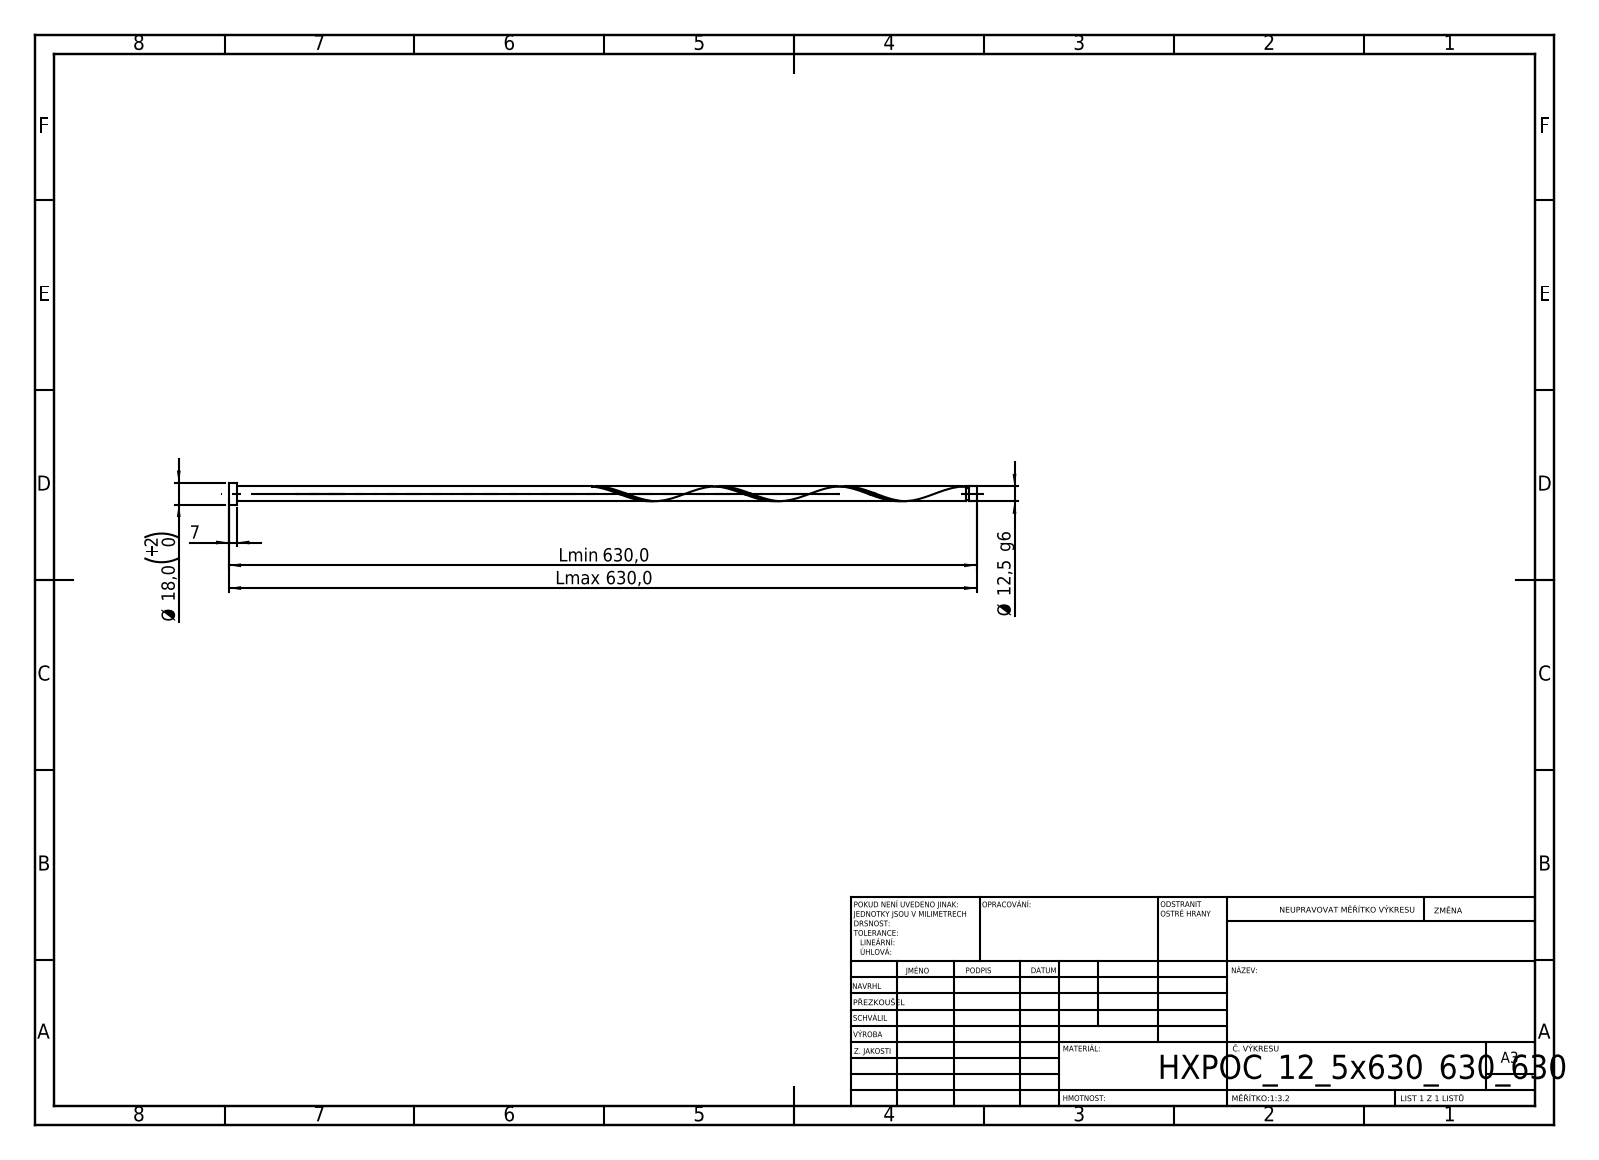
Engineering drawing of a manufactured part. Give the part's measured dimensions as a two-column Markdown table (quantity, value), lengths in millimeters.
| quantity | value |
| --- | --- |
| STEP written by | SolidWorks 2019 (CONFIG_CONTROL_DESIGN) |
| units | millimeters |
| bodies | 1 solid, 21 faces (6 planar, 14 cylindrical, 1 other) |
| overall size | 630 × 18 × 18 |
| volume | 77 384 mm³ |
| surface area | 25 845 mm² |
| round bosses / shafts (diameter × count) | 18 × 1, 12.5 × 1, 10 × 1 |
| main face-to-face distances | 7, 630, 623, 623.26, 616.26, 6.74, 620.76, 613.76, 2.5, 9.24 |
